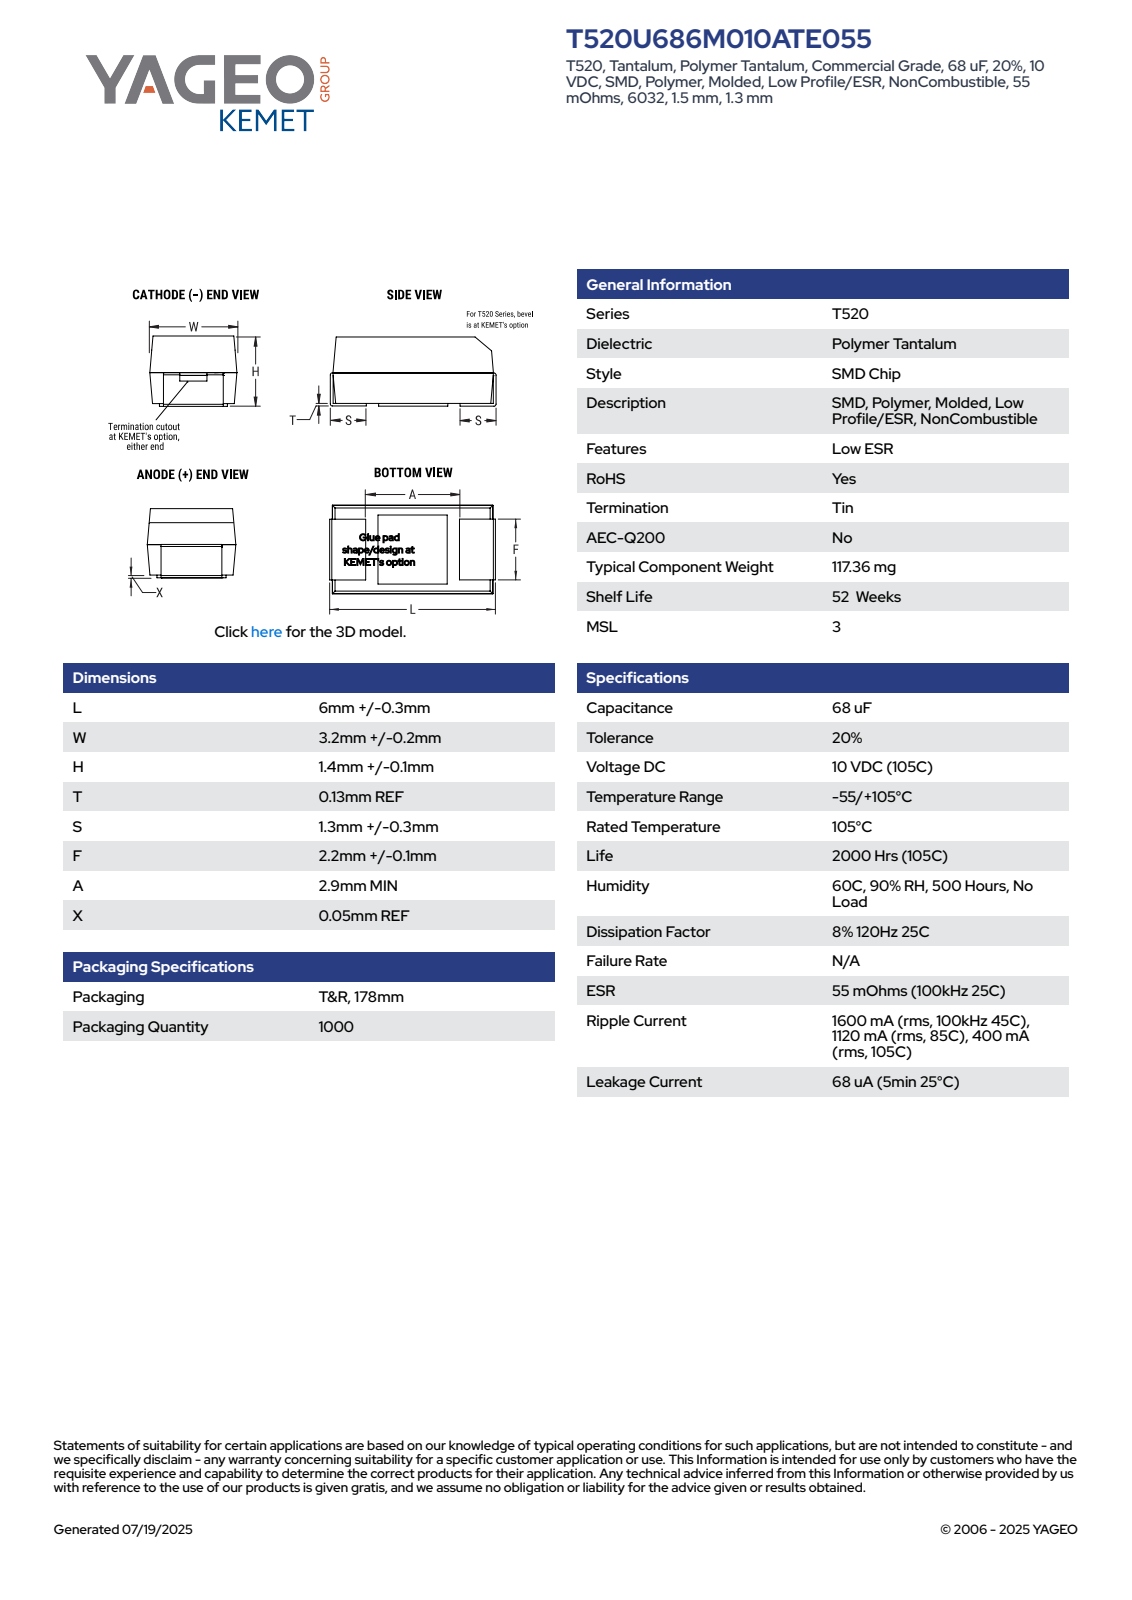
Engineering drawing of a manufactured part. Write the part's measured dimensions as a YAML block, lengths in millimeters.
part_name: "CTS_TCM2NOBNOKBOPT_6032_L6.3W3.4H1.5T0.13S1.3F2.3A2.9X0.05"
step_written_by: "SolidWorks 2014 (AUTOMOTIVE_DESIGN)"
units: millimeters
bodies: {solids: 4, faces: 90, planar: 86, cylindrical: 4, other: 0}
overall_size: [6.3, 3.4, 1.5]
volume: 28
surface_area: 75
partial_cylinders:
  - {radius: 0.13, count: 4}
face_to_face_distances: [1.42, 1.37, 1.5, 5.86, 3.35, 3.36, 6.17, 6.04, 6.3, 1.43]
